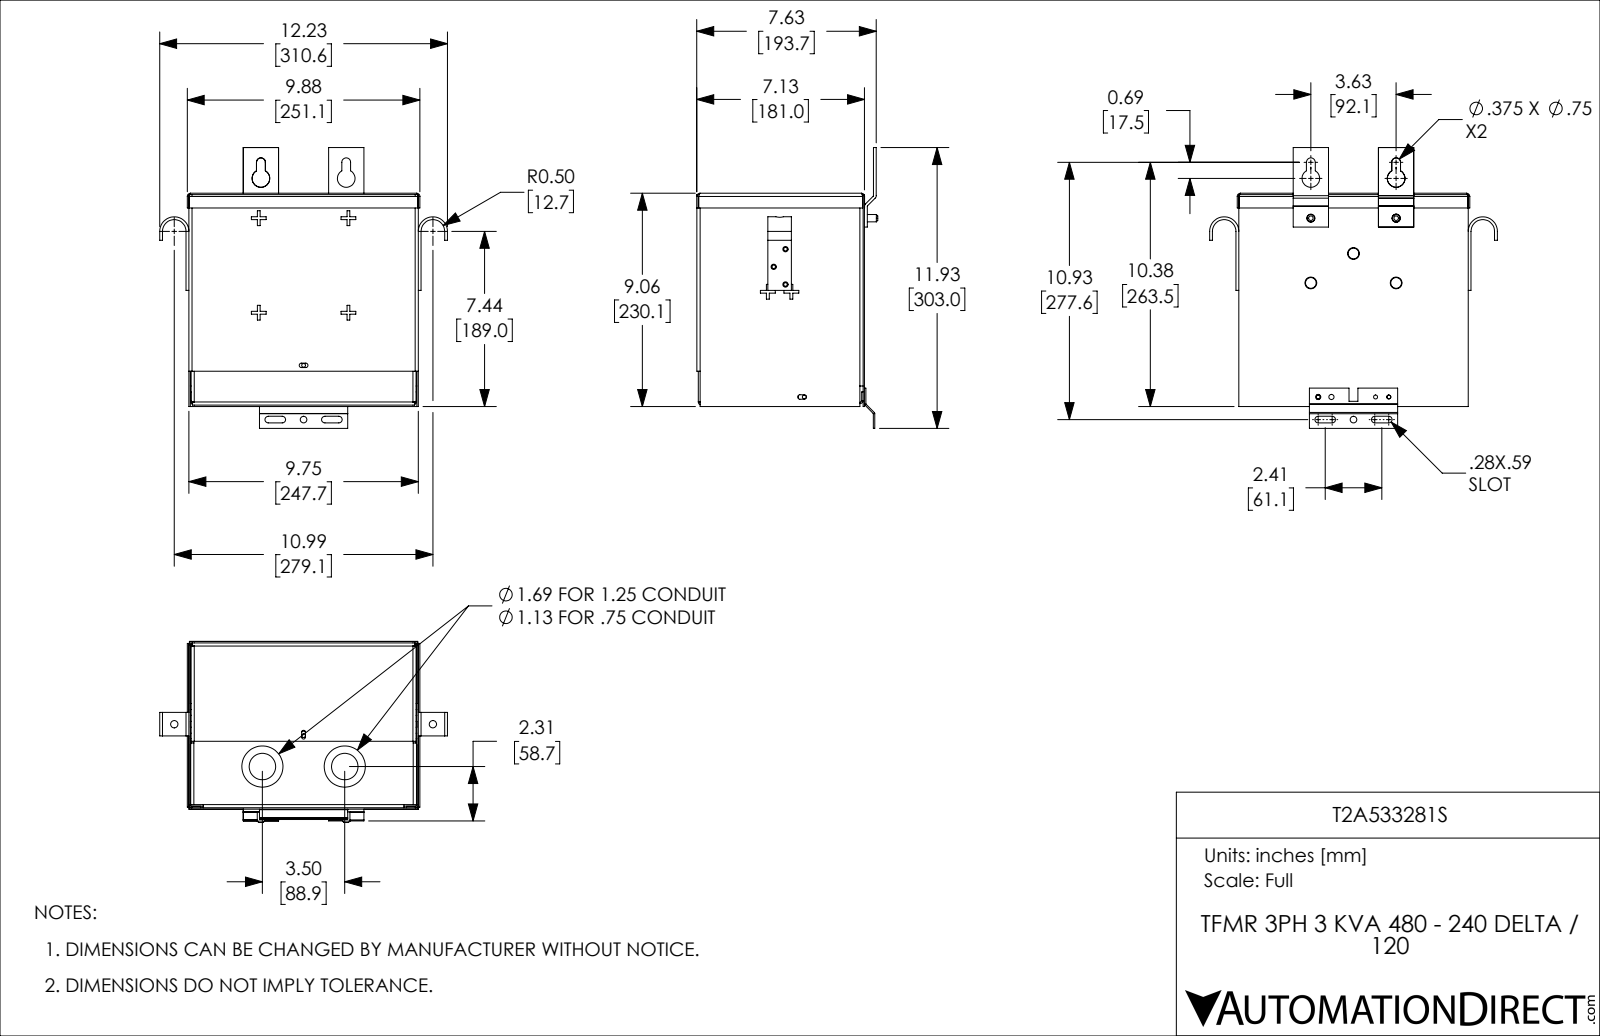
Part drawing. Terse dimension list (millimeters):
name: T2A533281S
written by: SolidWorks 2017 (AUTOMOTIVE_DESIGN)
unit: mm
bodies: 9 solids, 621 faces (405 planar, 144 cylindrical, 72 other)
size: 310.6 × 303 × 195.4
volume: 524 100 mm³; area: 661 900 mm²
holes: 5× ⌀4.1, 2× ⌀4.4, 2× ⌀5.6, 2× ⌀7.1, 2× ⌀8, 2× ⌀8.7, 2× ⌀19.1, 2× ⌀28.6, 2× ⌀44.5, 1× ⌀4.4, 1× ⌀4.7
bosses: 2× ⌀47.5, 2× ⌀31.6, 2× ⌀7.9
rounds: 16× R1.9, 16× R3.4, 8× R2.4, 4× R3.6, 2× R0.5, 2× R0.8, 2× R2, 2× R2
face distances: 1.5, 179.4, 1.5, 177.9, 227.1, 180.9, 246.1, 246.2, 247.7, 244.6
hole spacings: 14.3, 34.1, 41.6, 42.8, 45.2, 51.2, 55.5, 61.9
